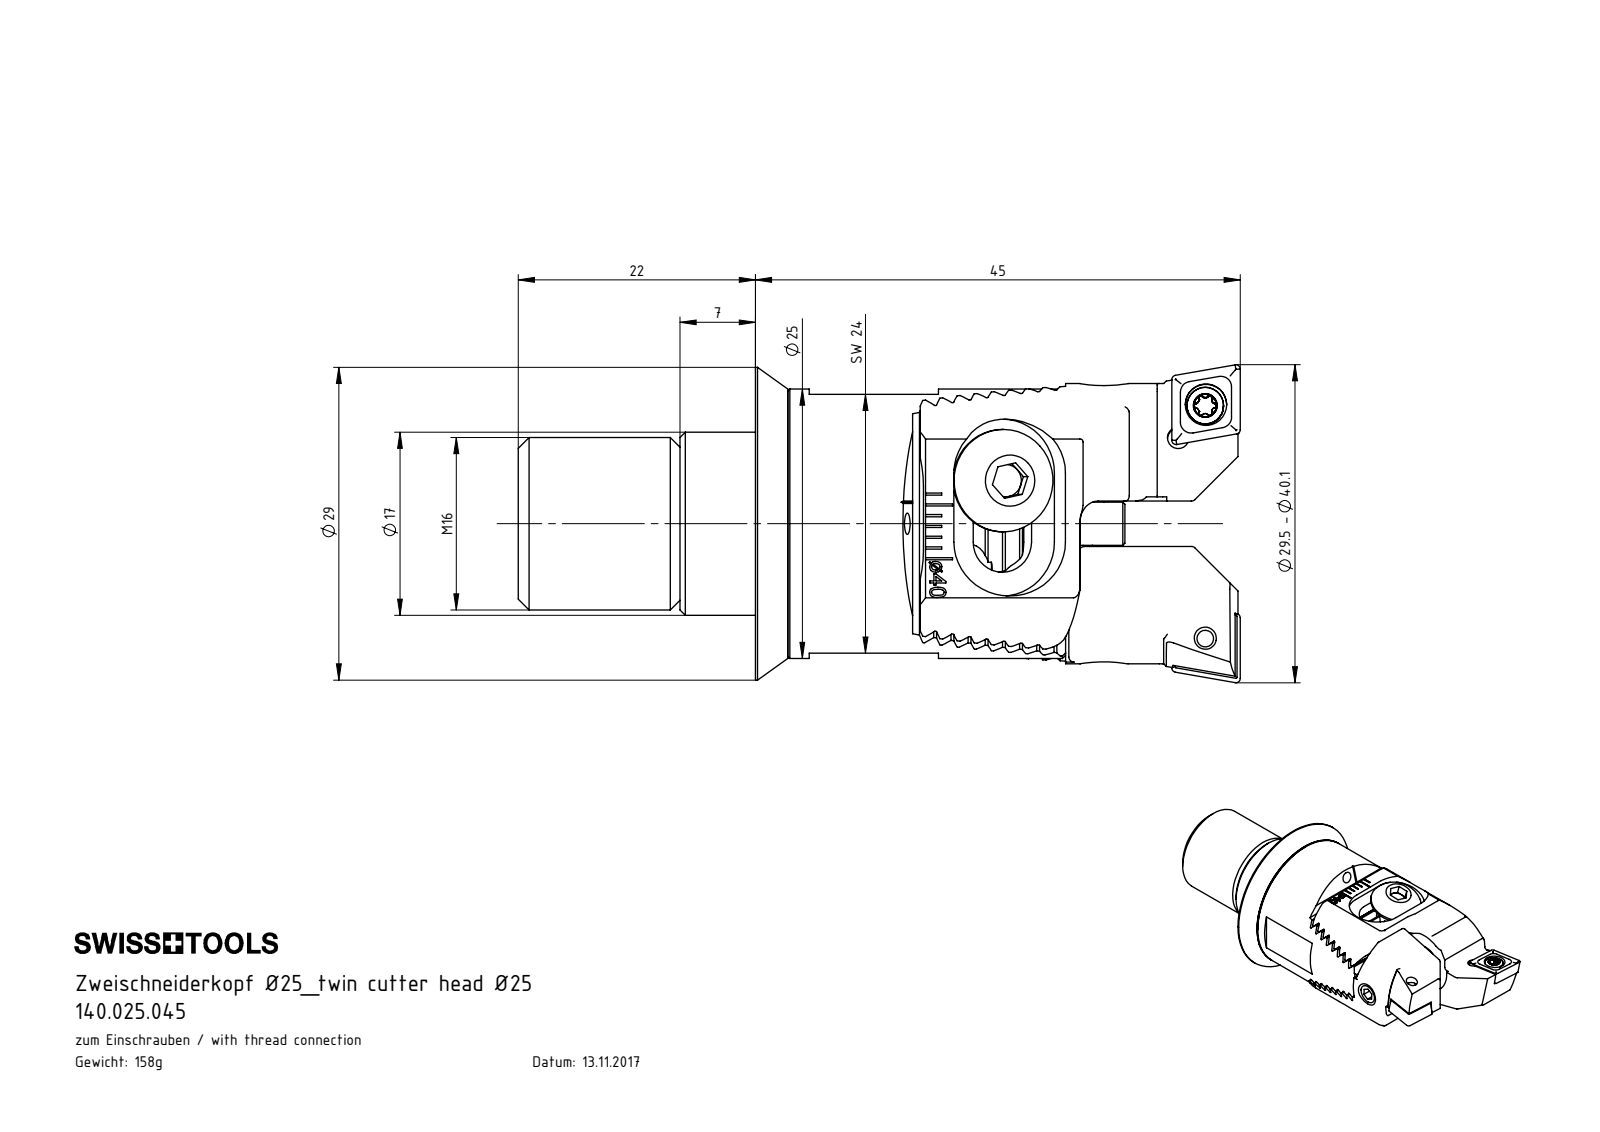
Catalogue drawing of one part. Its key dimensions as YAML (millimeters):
part_name: "D28-D25.HP5.003_A; Z25-ER1.001.012; Z20-ER2.001.013_A; HP5-ER2.012.030_A (+8 more)"
step_written_by: "SolidWorks 2017 (CONFIG_CONTROL_DESIGN)"
units: millimeters
bodies: {solids: 17, faces: 1044, planar: 504, cylindrical: 256, other: 284}
overall_size: [67, 29.5, 29]
volume: 20663
surface_area: 14861
round_holes:
  - {diameter: 2, count: 6}
  - {diameter: 1.6, count: 2}
  - {diameter: 2.05, count: 2}
  - {diameter: 2.8, count: 2}
  - {diameter: 3.85, count: 2}
  - {diameter: 4.2, count: 2}
  - {diameter: 6, count: 2}
  - {diameter: 2.5, count: 1}
  - {diameter: 3.3, count: 1}
  - {diameter: 3.5, count: 1}
  - {diameter: 5.3, count: 1}
  - {diameter: 10.6, count: 1}
round_bosses_or_shafts:
  - {diameter: 9.5, count: 2}
  - {diameter: 5, count: 2}
  - {diameter: 4, count: 2}
  - {diameter: 3.4, count: 2}
  - {diameter: 2.5, count: 2}
  - {diameter: 29, count: 1}
  - {diameter: 28, count: 1}
  - {diameter: 25, count: 1}
partial_cylinders:
  - {radius: 0.12, count: 18}
  - {radius: 0.5, count: 18}
  - {radius: 0.12, count: 16}
  - {radius: 0.21, count: 12}
  - {radius: 0.36, count: 10}
  - {radius: 2, count: 4}
  - {radius: 2.8, count: 4}
  - {radius: 5, count: 4}
face_to_face_distances: [1.43, 3, 2.86, 7.14, 5.71, 1.39, 1.47, 8.57, 4.28, 10]
hole_center_spacings: [3.91, 4.01, 7, 19.06, 19.15, 21.97, 13.52, 15.9]
